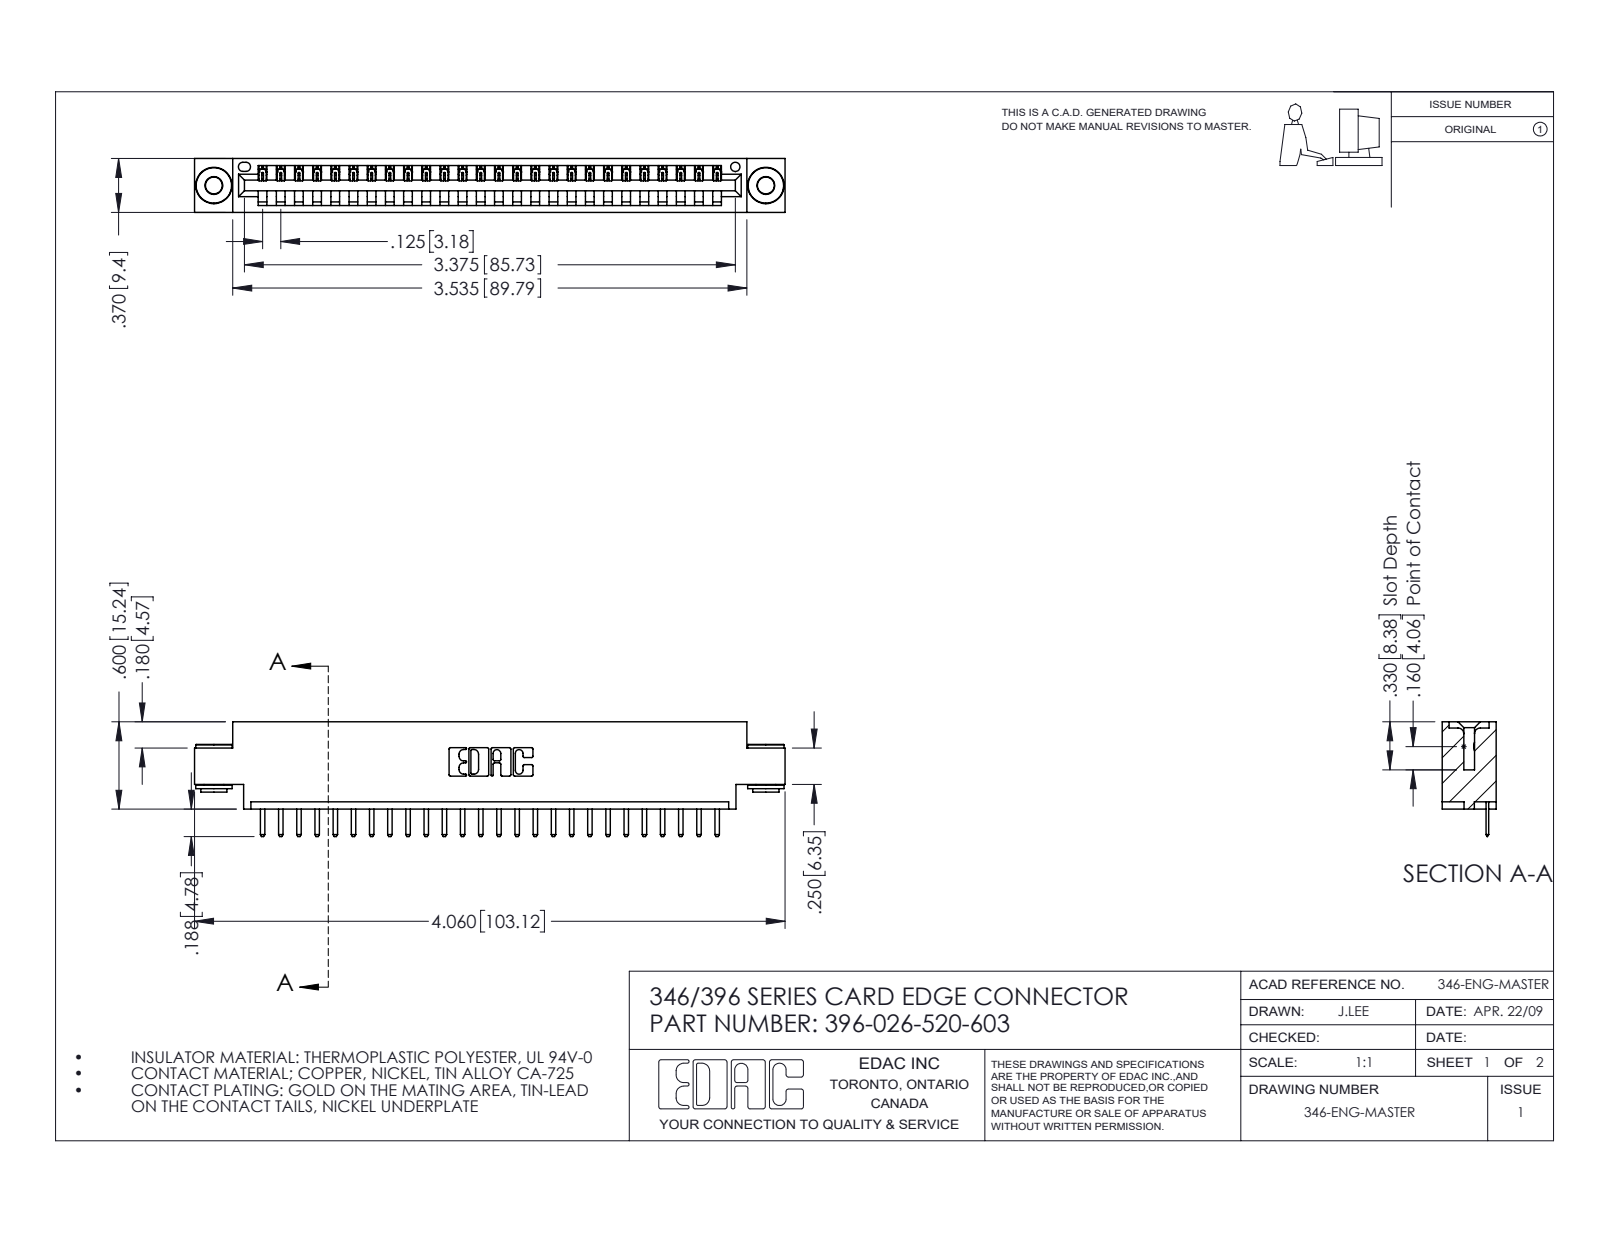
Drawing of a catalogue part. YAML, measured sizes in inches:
part_name: "346 Part_0.170 Offset - 0.156 Dia-TH; 396-026-520-603; 345-292-001_345-293-120; 345-250-002_345-250-002-102"
step_written_by: "SolidWorks 2016 (CONFIG_CONTROL_DESIGN)"
units: inches
bodies: {solids: 29, faces: 1776, planar: 1182, cylindrical: 586, other: 8}
overall_size: [4.06, 0.788, 0.37]
volume: 0.583
surface_area: 18.44
round_holes:
  - {diameter: 0.116, count: 2}
  - {diameter: 0.156, count: 2}
  - {diameter: 0.064, count: 1}
round_bosses_or_shafts:
  - {diameter: 0.25, count: 2}
  - {diameter: 0.18, count: 2}
  - {diameter: 0.136, count: 2}
partial_cylinders:
  - {radius: 0.01, count: 54}
  - {radius: 0.006, count: 52}
  - {radius: 0.01, count: 22}
  - {radius: 0.007, count: 6}
  - {radius: 0.031, count: 6}
  - {radius: 0.026, count: 3}
  - {radius: 0.031, count: 2}
  - {radius: 0.04, count: 2}
face_to_face_distances: [0.37, 0.048, 0.322, 0.25, 0.025, 0.148, 0.222, 0.1, 0.174, 0.072]
hole_center_spacings: [0.246, 3.587, 3.795]
